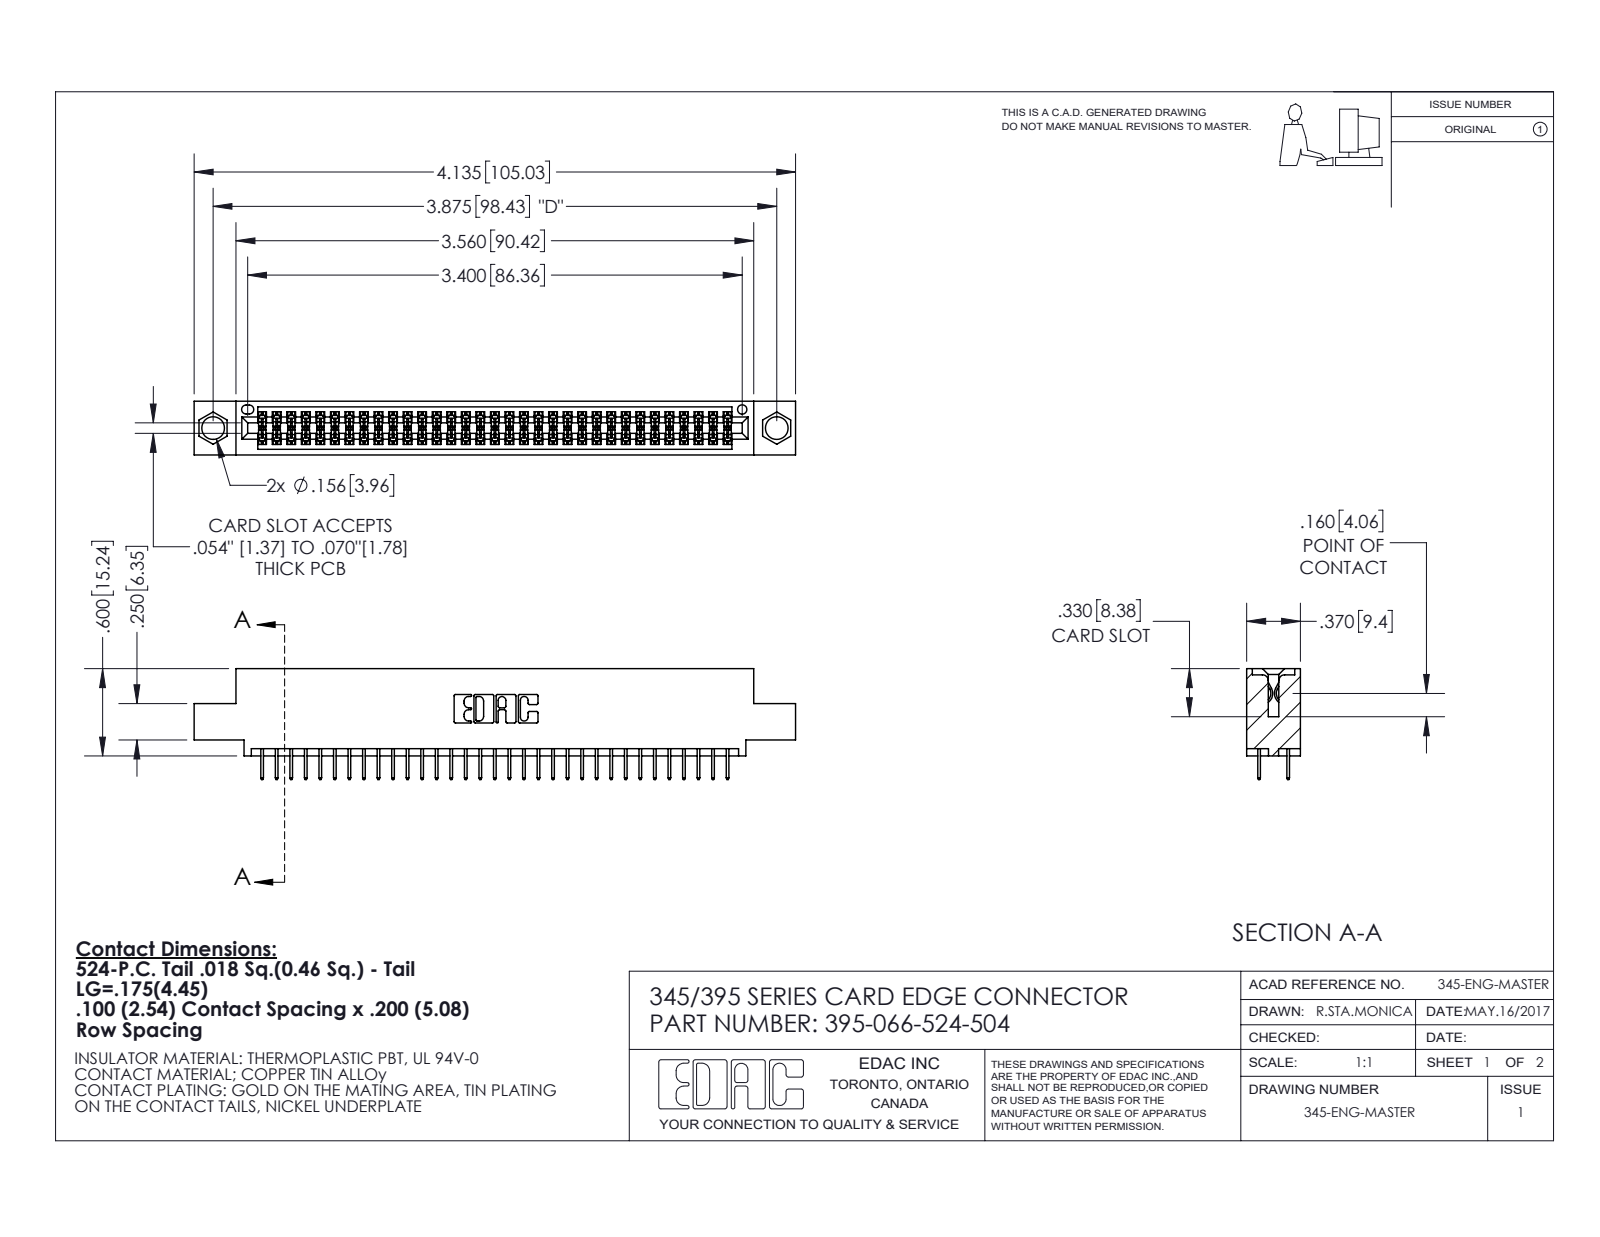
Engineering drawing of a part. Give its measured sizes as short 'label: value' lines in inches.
name: 345 Part_0.110 Offset - 0.156 Dia-TI; 395-066-524-504; 345-292-001_345-293-124
written by: SolidWorks 2020 (CONFIG_CONTROL_DESIGN)
unit: in
bodies: 67 solids, 3708 faces (2672 planar, 1036 cylindrical, 0 other)
size: 4.135 × 0.762 × 0.37
volume: 0.6 in³; area: 21.78 in²
holes: 2× ⌀0.156, 1× ⌀0.064
rounds: 99× R0.006, 22× R0.01, 6× R0.007, 6× R0.031, 3× R0.026, 2× R0.014, 2× R0.019, 2× R0.022
face distances: 0.072, 0.298, 0.2, 0.37, 0.098, 0.272, 0.025, 0.225, 0.072, 0.175
hole spacings: 0.27, 3.64, 3.875
